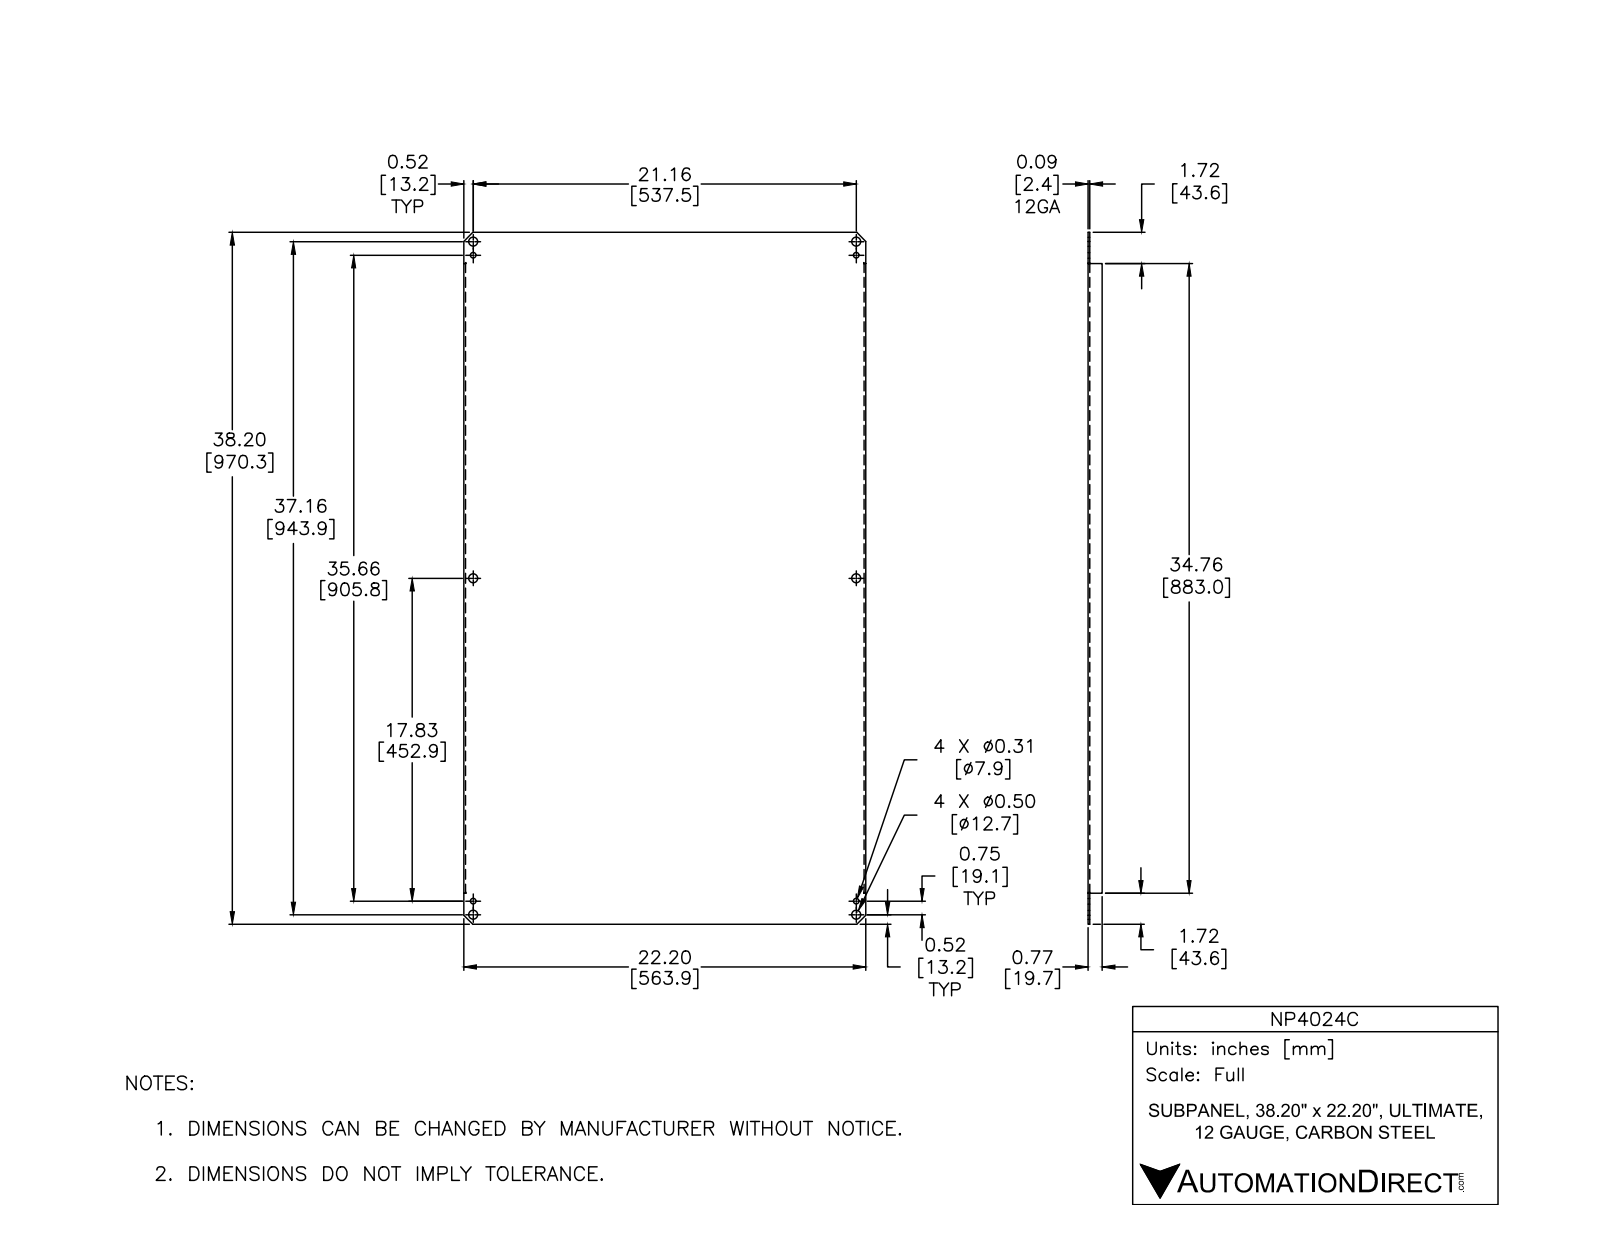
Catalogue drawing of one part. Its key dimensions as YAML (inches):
part_name: "NP4024C"
step_written_by: "Autodesk Inventor 2012 (AUTOMOTIVE_DESIGN)"
units: inches
bodies: {solids: 1, faces: 44, planar: 30, cylindrical: 14, other: 0}
overall_size: [38.2, 22.2, 0.774]
volume: 83.58
surface_area: 1796
round_holes:
  - {diameter: 0.5, count: 6}
  - {diameter: 0.313, count: 4}
partial_cylinders:
  - {radius: 0.016, count: 2}
  - {radius: 0.109, count: 2}
face_to_face_distances: [0.094, 22.106, 22.2, 22.013, 0.68, 0.774, 38.2, 1.718, 36.482, 34.764]
hole_center_spacings: [21.16, 0.75, 17.83, 18.58, 21.173, 27.67, 28.159, 36.41]
